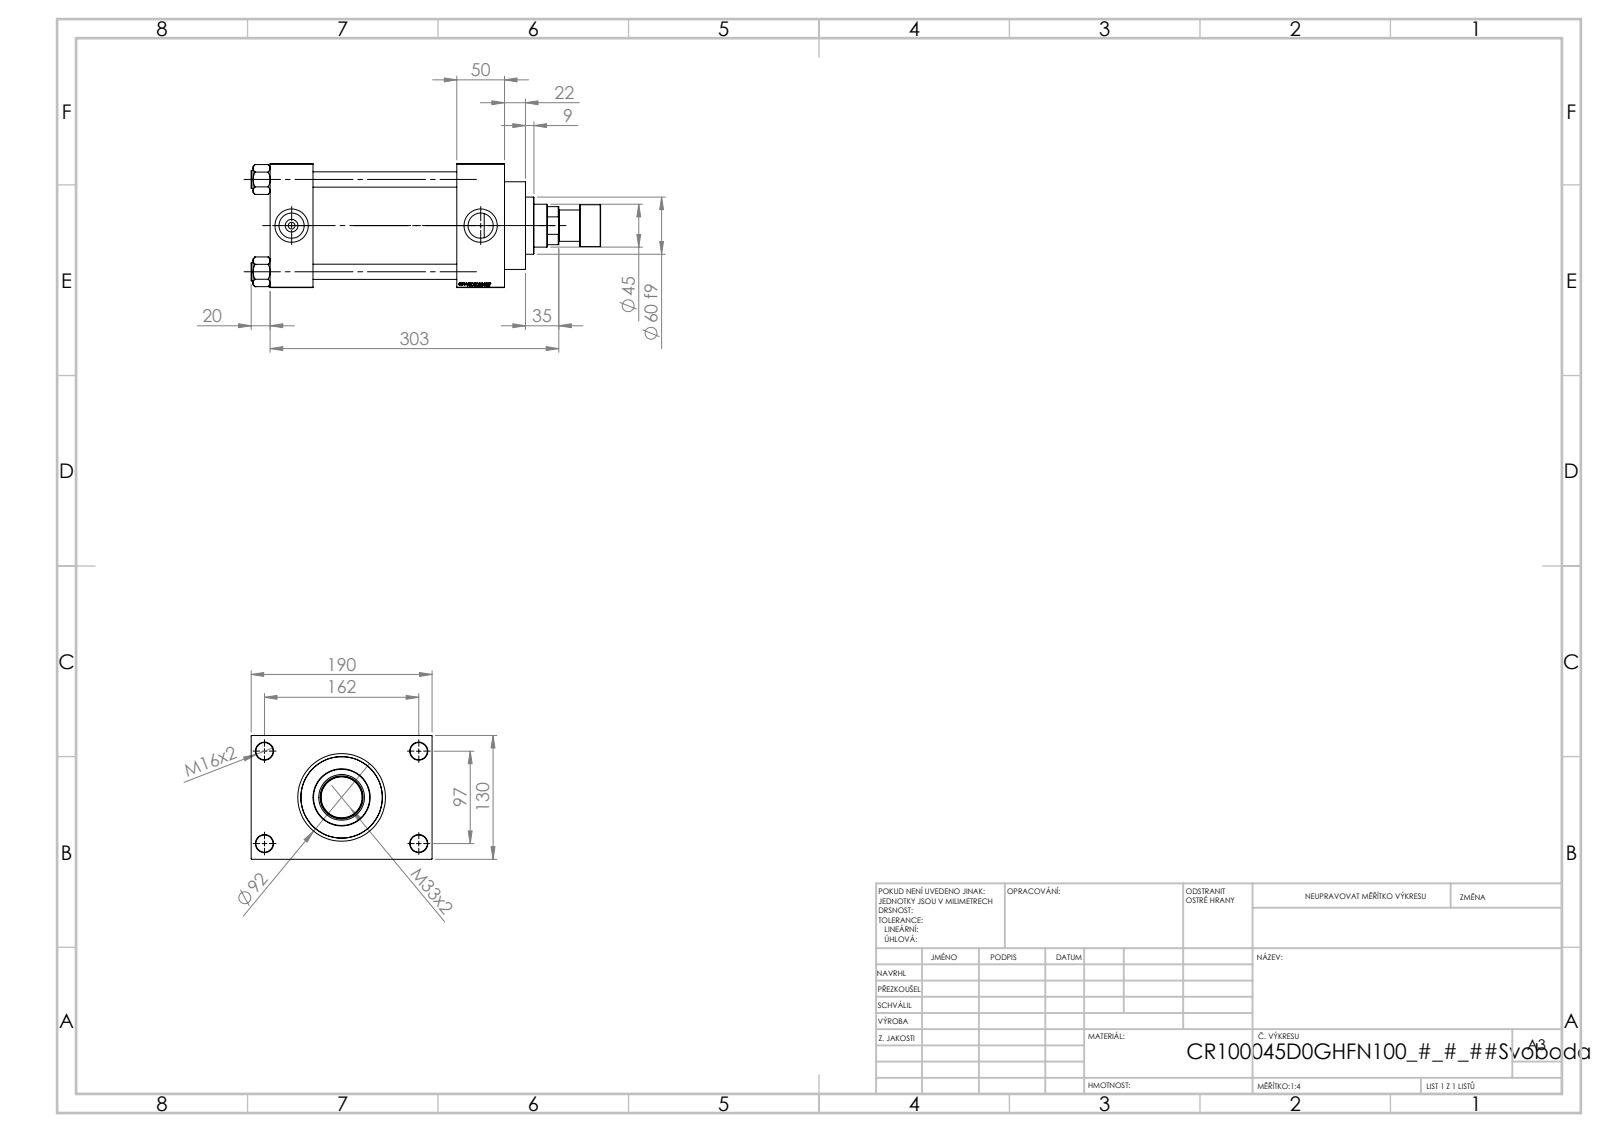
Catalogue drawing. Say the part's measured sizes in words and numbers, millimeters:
The part is named "V215CR_VCP_D; V215CR_D_Body; V215_VC_A; V215CR_D_TYCINKA (+2 more)". Its 3-D file was written by "SolidWorks 2019 (CONFIG_CONTROL_DESIGN)". It is 12 solids with 1164 faces: 548 planar, 92 cylindrical and 524 other. Overall it measures 367 by 190 by 130 millimeters. Its volume is 2 912 000 cubic millimeters and its surface area 442 424 square millimeters. Round holes: 4 of diameter 16, 4 of diameter 18, 2 of diameter 7, 2 of diameter 26.44, 2 of diameter 35, 1 of diameter 31.5, 1 of diameter 45, 1 of diameter 48, 1 of diameter 76, 1 of diameter 85.5, 1 of diameter 100. Round bosses or shafts: 4 of diameter 19, 1 of diameter 106, 1 of diameter 92, 1 of diameter 60, 1 of diameter 44, 1 of diameter 33. The main face-to-face distances are 130, 151, 45, 196, 246, 201, 50, 30, 160, 96. The hole center spacings are 32.55, 68.52, 94.41, 96.9, 102.27, 129.45, 161.73, 97.
